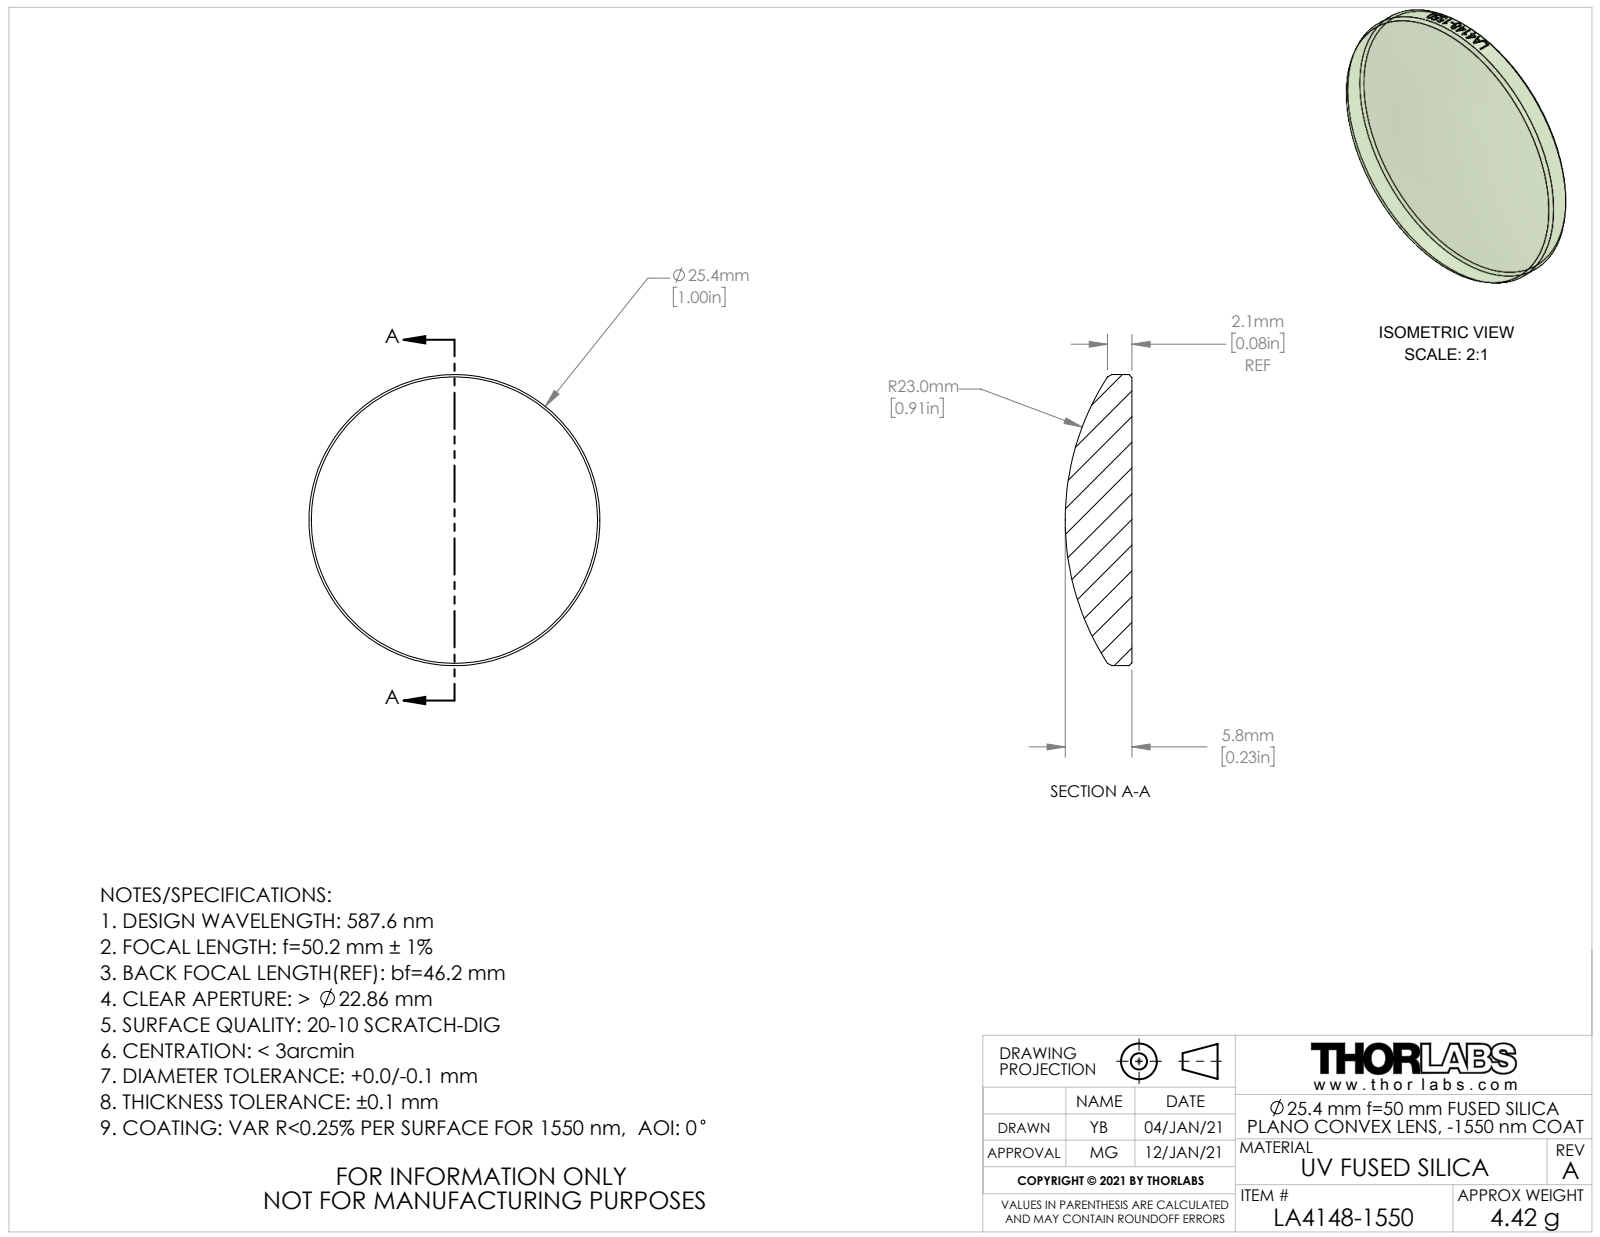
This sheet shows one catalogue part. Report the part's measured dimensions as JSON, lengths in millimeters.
{"part_name": "CTN015955-E0W", "step_written_by": "SolidWorks 2018 (AUTOMOTIVE_DESIGN)", "units": "millimeters", "bodies": {"solids": 1, "faces": 26, "planar": 1, "cylindrical": 19, "other": 6}, "overall_size": [25.4, 25.4, 5.8], "volume_mm3": 2000, "surface_area_mm2": 1202, "round_bosses_or_shafts": [[25.4, 1]]}
